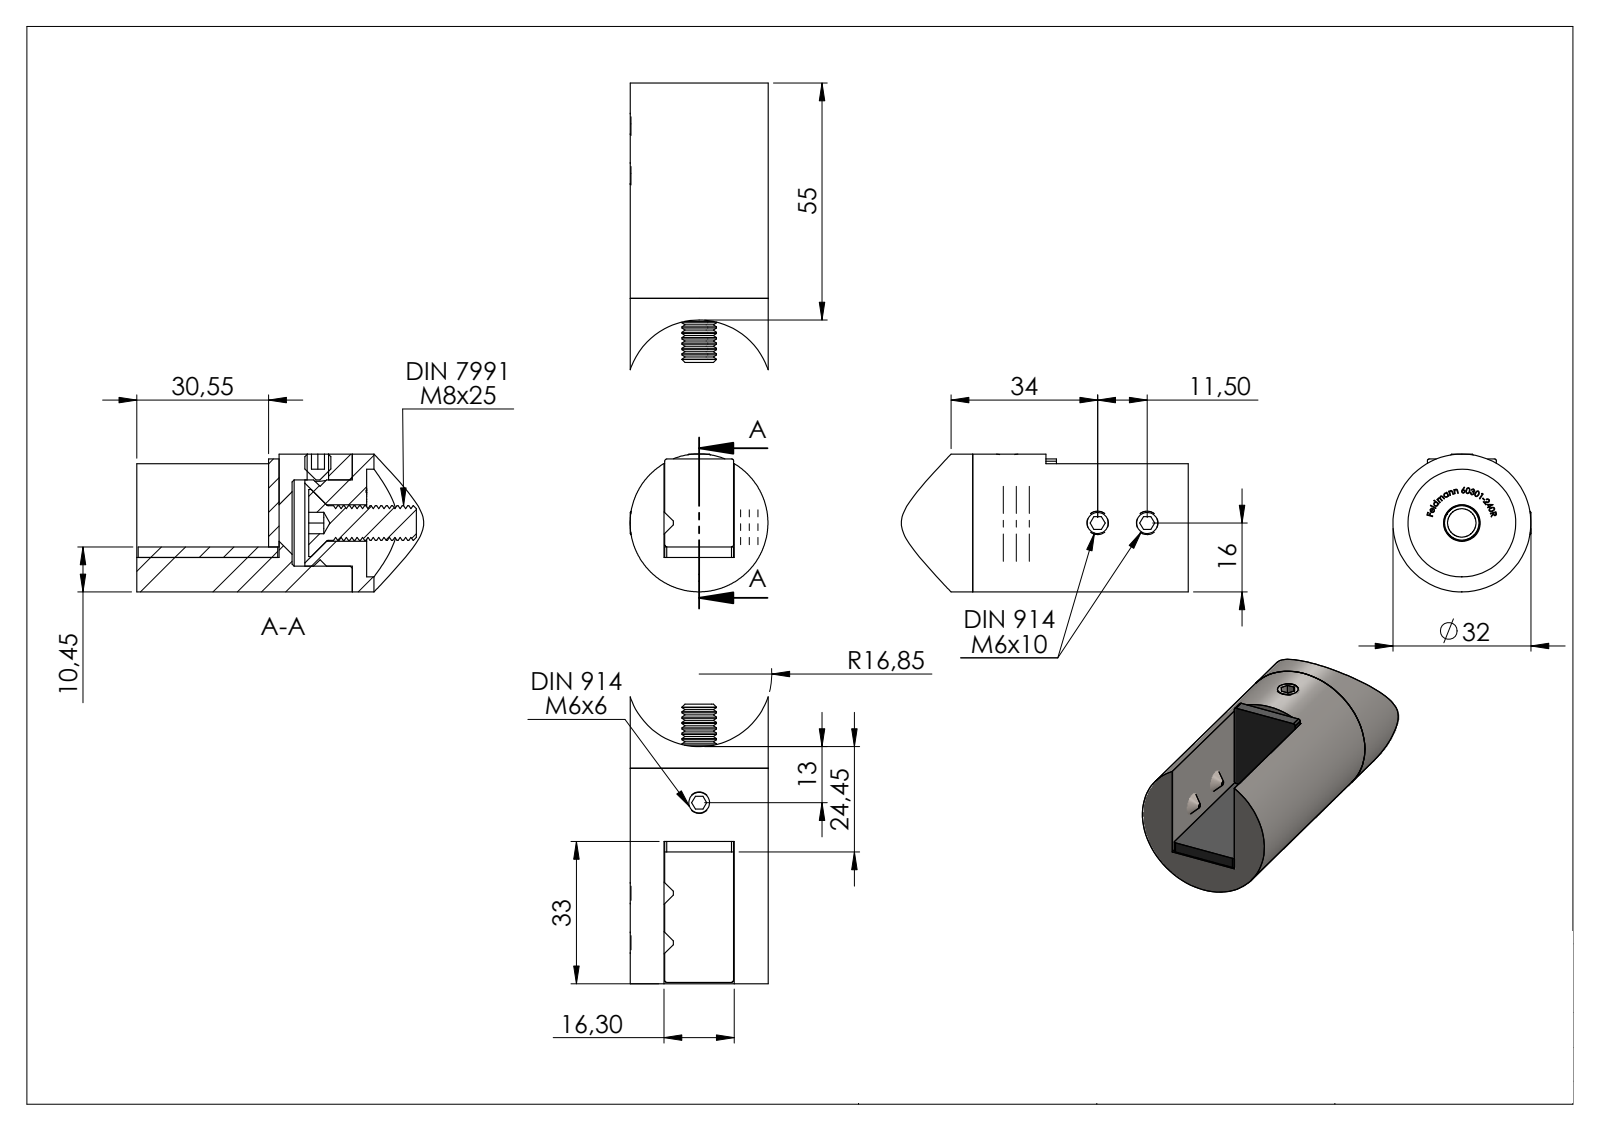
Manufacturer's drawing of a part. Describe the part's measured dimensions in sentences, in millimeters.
The part is named "60301-240R; socket countersunk head screw_din; socket set screw cone point_din_DIN 914 - M6 x 10-S; socket set screw cone point_din (+8 more)". Its 3-D file was written by "SolidWorks 2018 (CONFIG_CONTROL_DESIGN)". It is 8 solids with 434 faces: 190 planar, 53 cylindrical and 191 other. Overall it measures 70 by 64.85 by 32 millimeters. Its volume is 32 395 cubic millimeters and its surface area 16 864 square millimeters. Round holes: 3 of diameter 5, 1 of diameter 8.5, 1 of diameter 25. Round bosses or shafts: 3 of diameter 6, 1 of diameter 32, 1 of diameter 20, 1 of diameter 15.57, 1 of diameter 8. Partial cylindrical surfaces (rounded edges, fillets, slot ends): 8 of radius 0.5, 1 of radius 24.15. The main face-to-face distances are 2.45, 16.3, 17, 3.3, 20.3, 53.3, 50, 33, 22.75, 19.45. The hole center spacings are 11.5.
